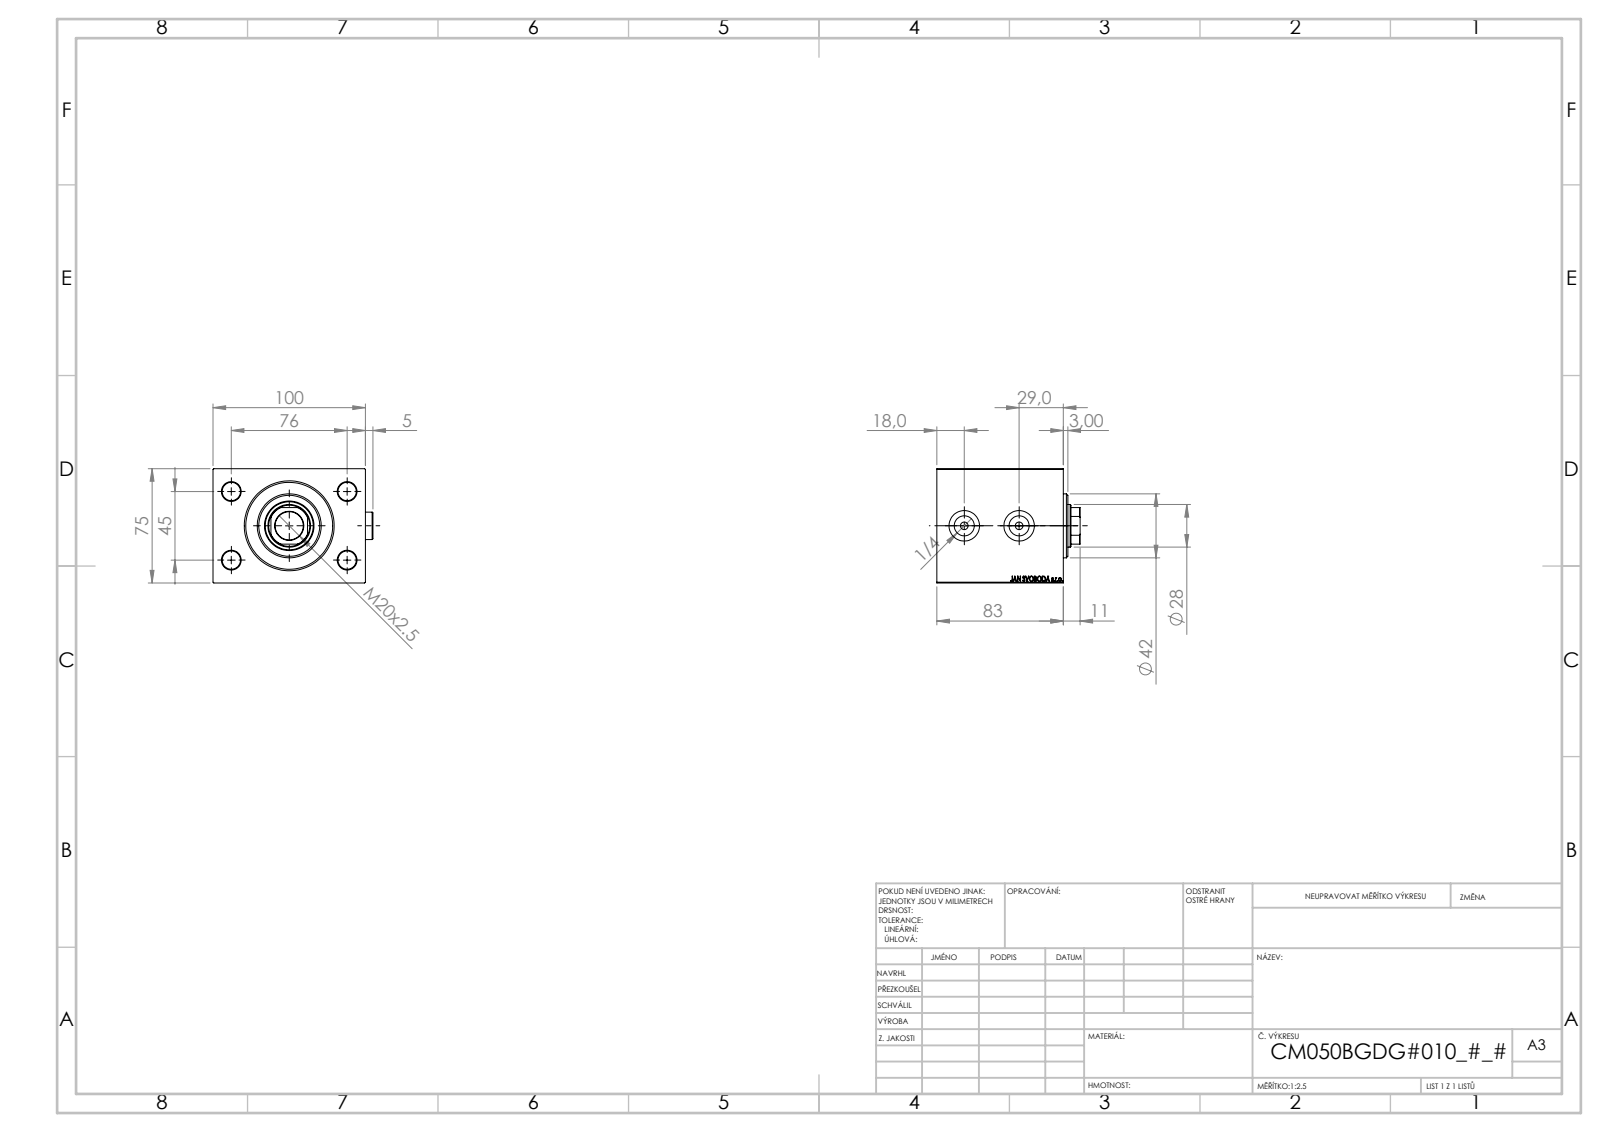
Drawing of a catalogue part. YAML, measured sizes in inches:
part_name: "V450CM_VC_B; V450CM_B_VCP; Zatka_OIL_PORT; V450CM_B_Body"
step_written_by: "SolidWorks 2019 (CONFIG_CONTROL_DESIGN)"
units: inches
bodies: {solids: 5, faces: 936, planar: 436, cylindrical: 70, other: 430}
overall_size: [4.13, 3.701, 2.953]
volume: 35.63
surface_area: 132.8
round_holes:
  - {diameter: 0.472, count: 4}
  - {diameter: 0.197, count: 2}
  - {diameter: 0.518, count: 2}
  - {diameter: 0.787, count: 2}
  - {diameter: 0.728, count: 1}
  - {diameter: 1.102, count: 1}
  - {diameter: 1.24, count: 1}
  - {diameter: 1.28, count: 1}
  - {diameter: 1.969, count: 1}
  - {diameter: 2.047, count: 1}
  - {diameter: 2.244, count: 1}
round_bosses_or_shafts:
  - {diameter: 0.709, count: 2}
  - {diameter: 1.654, count: 1}
partial_cylinders:
  - {radius: 0.531, count: 1}
face_to_face_distances: [2.953, 3.937, 3.268, 1.26, 2.008, 0.85, 1.157, 2.417, 0.394, 1.244]
hole_center_spacings: [1.739, 1.772, 2.992, 3.477, 1.417]
